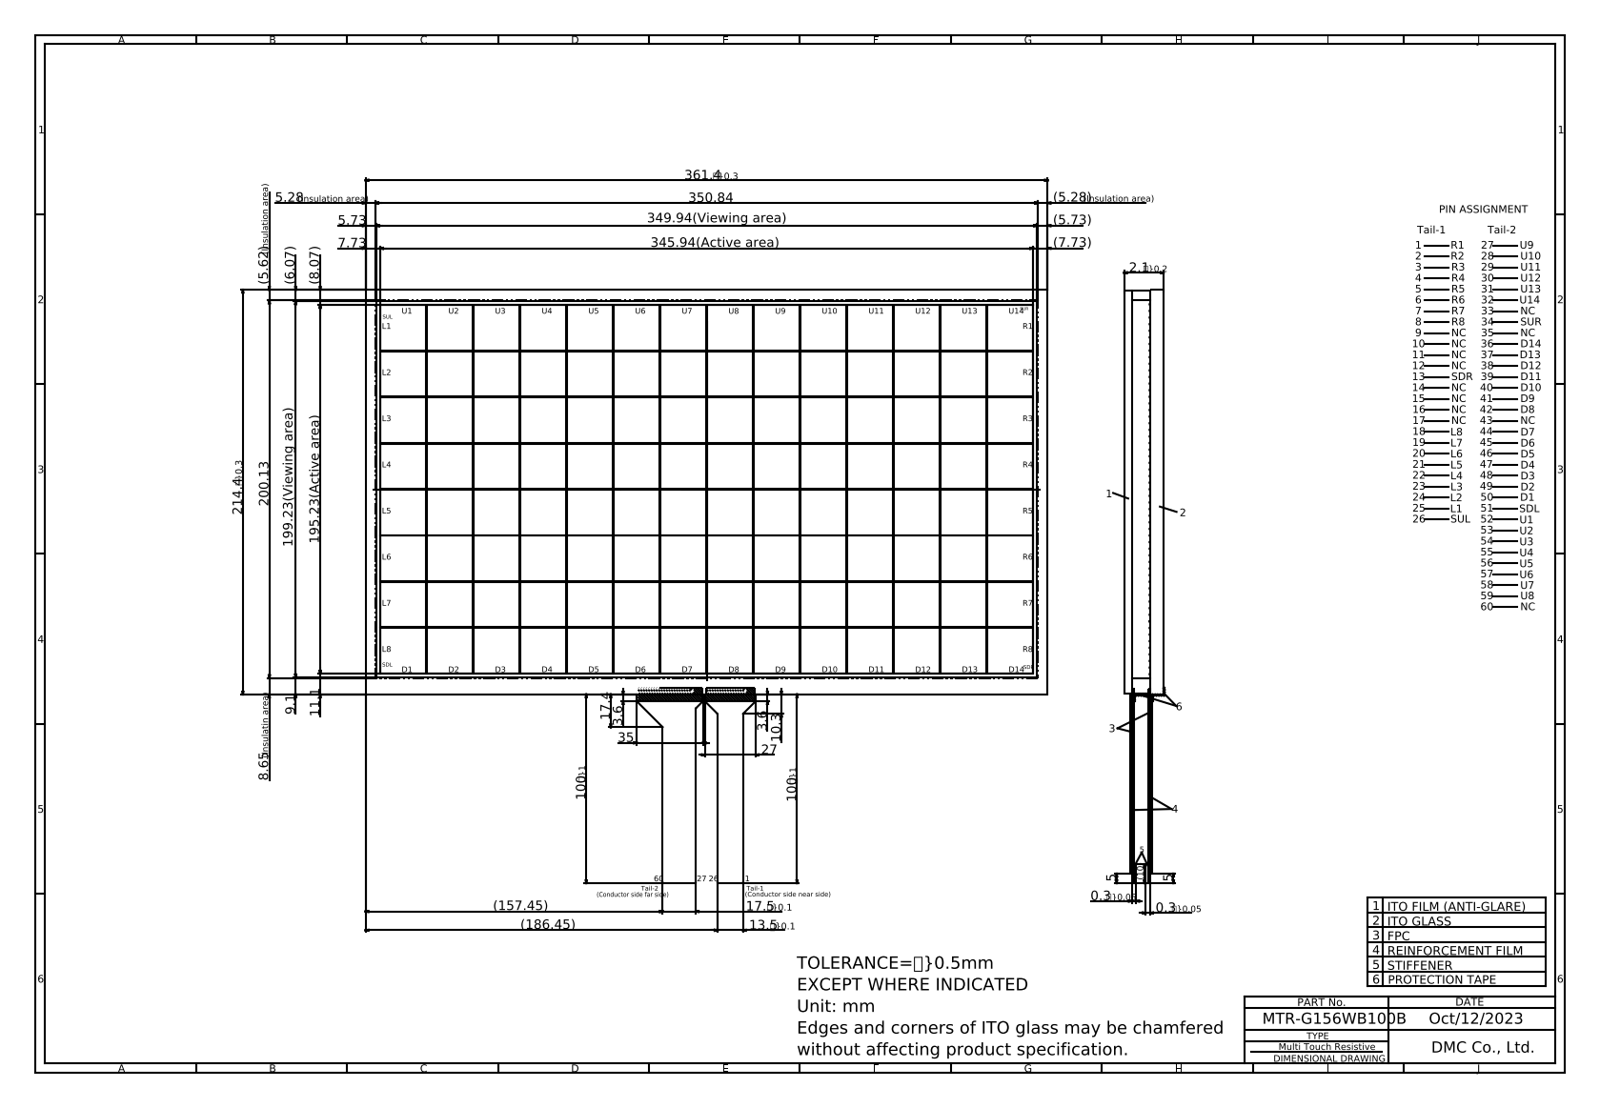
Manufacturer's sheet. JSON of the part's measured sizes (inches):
{"part_name": "MTR-G156WB100B", "step_written_by": "Autodesk Inventor 2020 (CONFIG_CONTROL_DESIGN)", "units": "inches", "bodies": {"solids": 1, "faces": 294, "planar": 282, "cylindrical": 12, "other": 0}, "overall_size": [19.92, 14.066, 0.087], "volume_in3": 9.941, "surface_area_in2": 254.8, "partial_cylinders_radius": [[0.039, 8], [0.008, 4]], "face_to_face_distances": [0.083, 0.071, 0.075, 0.079, 8.441, 14.228, 0.016, 0.087, 0.02, 0.028]}
